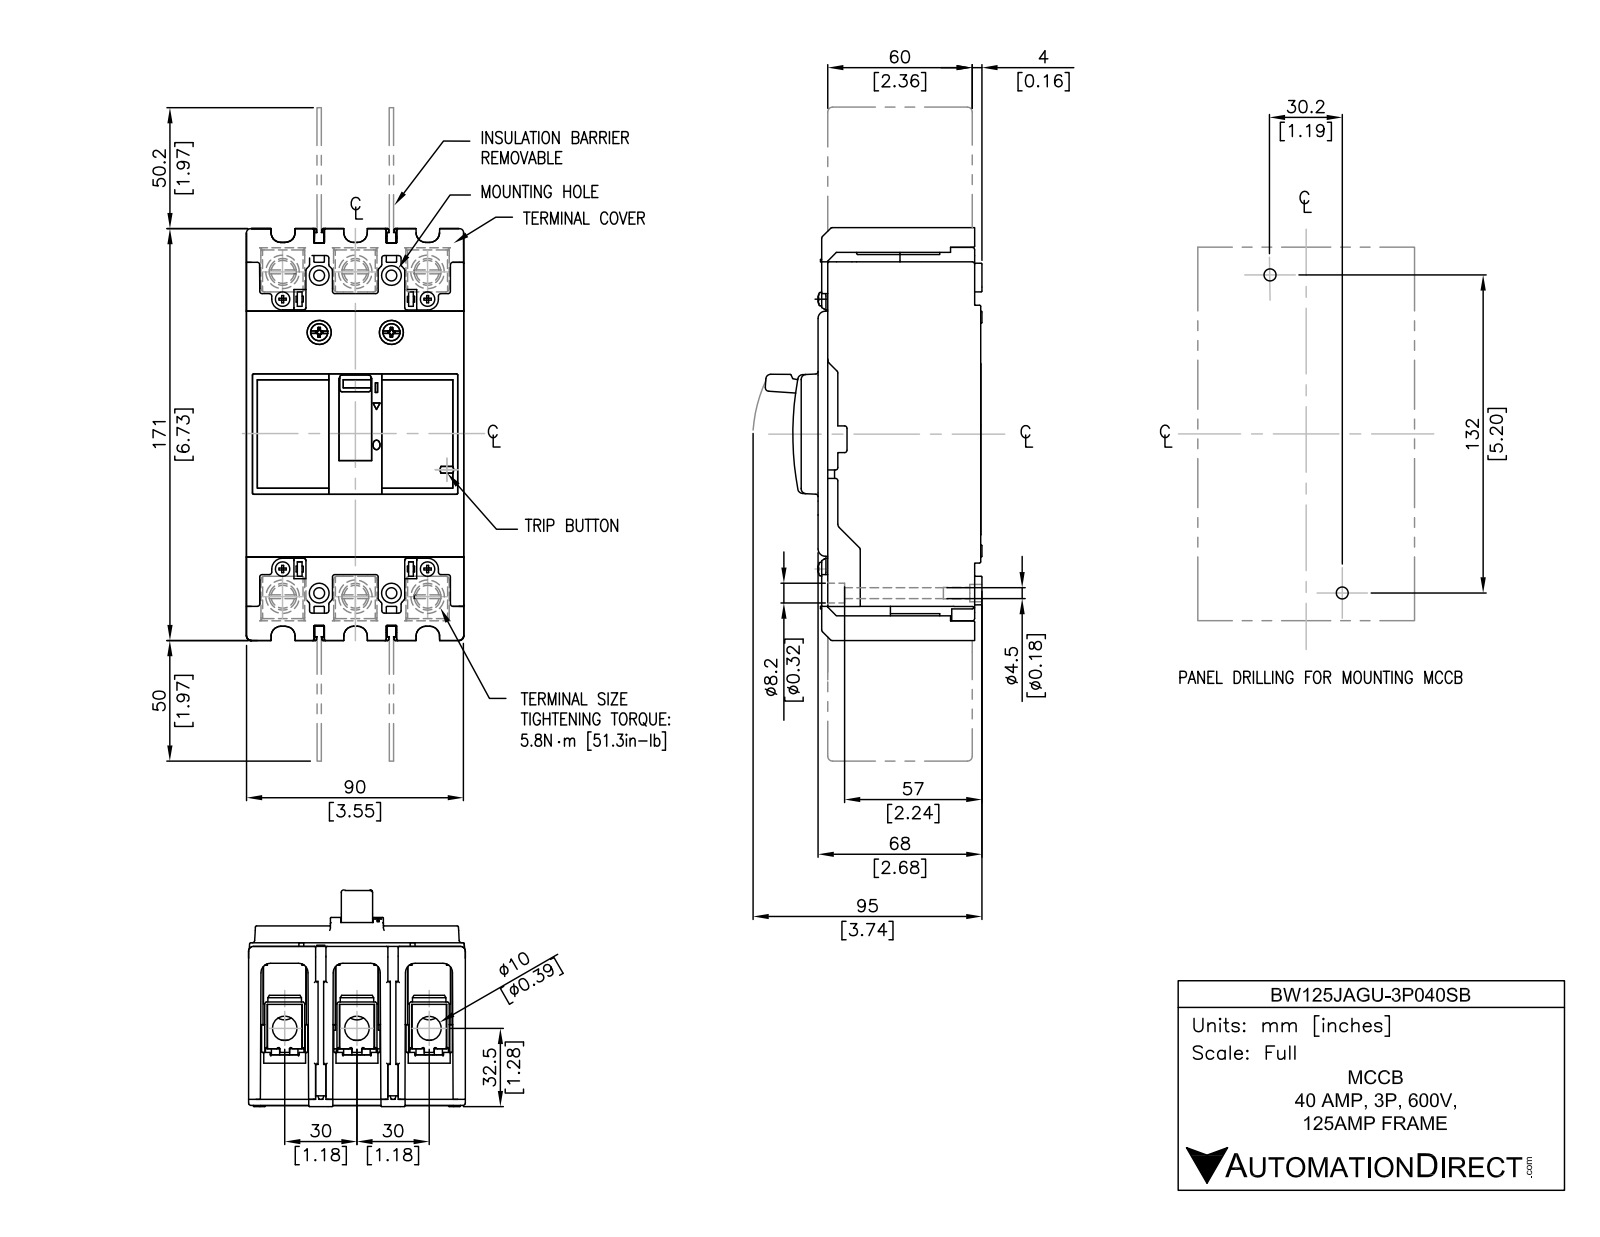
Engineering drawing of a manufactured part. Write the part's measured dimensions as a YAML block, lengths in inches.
part_name: "BW125JAGU-3P040SB"
step_written_by: "SolidWorks 2018 (AUTOMOTIVE_DESIGN)"
units: inches
bodies: {solids: 14, faces: 452, planar: 340, cylindrical: 88, other: 24}
overall_size: [10.197, 3.602, 3.543]
volume: 57.4
surface_area: 230.3
round_holes:
  - {diameter: 0.315, count: 6}
  - {diameter: 0.177, count: 4}
  - {diameter: 0.323, count: 4}
round_bosses_or_shafts:
  - {diameter: 0.472, count: 6}
partial_cylinders:
  - {radius: 0.157, count: 12}
  - {radius: 0.079, count: 6}
  - {radius: 0.118, count: 6}
face_to_face_distances: [1.181, 1.11, 1.252, 2.291, 2.433, 0.142, 3.543, 0.236, 2.402, 1.039]
hole_center_spacings: [0.593, 5.289, 1.181, 1.772, 5.444, 5.546, 5.315, 2.362]
